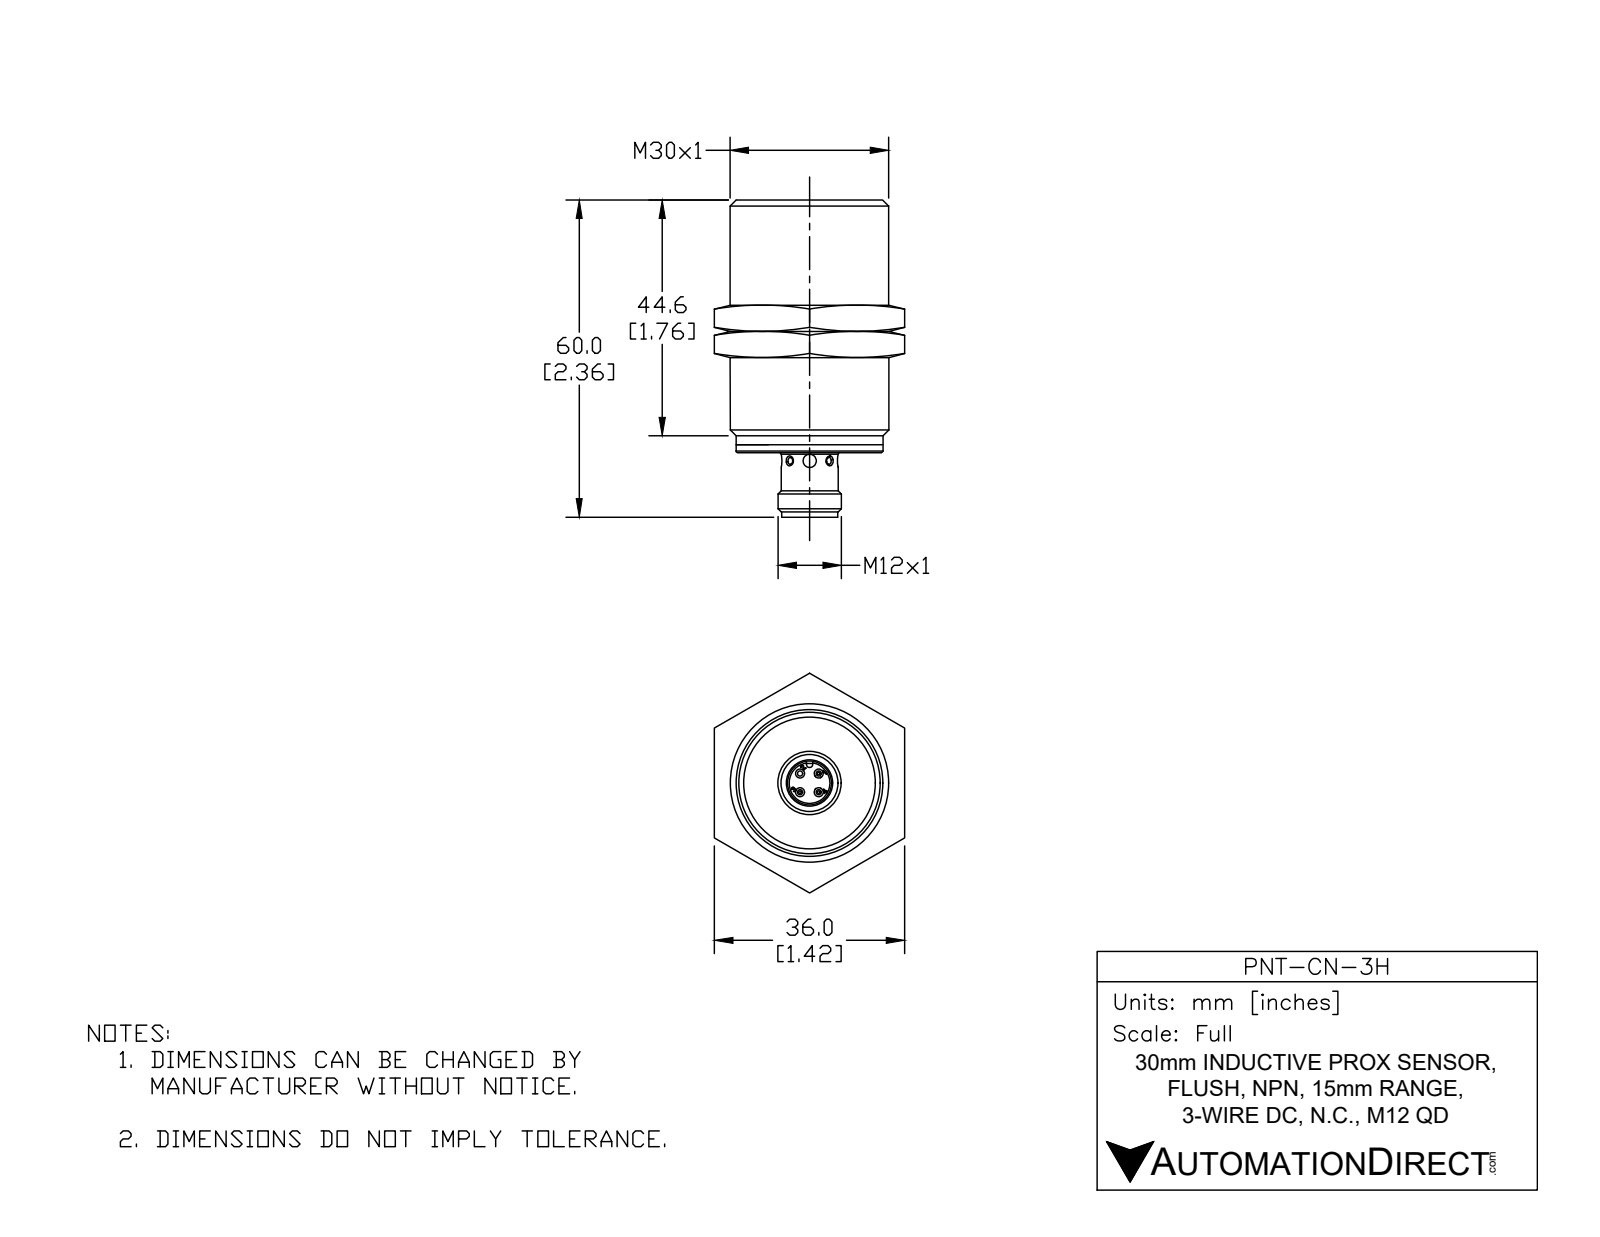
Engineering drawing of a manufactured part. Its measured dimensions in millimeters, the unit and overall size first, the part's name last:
Units: millimetres
Overall size (bounding box): 60 × 30 × 30
Round holes (diameter × count): ⌀1.1 ×3, ⌀1 ×2, ⌀2.5 ×2, ⌀1 ×1, ⌀1 ×1, ⌀8.2 ×1, ⌀8.3 ×1, ⌀10 ×1, ⌀26.6 ×1, ⌀27.3 ×1
Round bosses / shafts (diameter × count): ⌀1 ×9, ⌀30 ×1, ⌀27.8 ×1, ⌀27.5 ×1, ⌀27.3 ×1, ⌀26.5 ×1, ⌀26.3 ×1, ⌀25.9 ×1
Partial cylindrical surfaces — rounded edges, fillets, slot ends (radius × count): R0.1 ×12, R0.5 ×8, R4 ×6, R0.8 ×3, R1 ×3, R0.6 ×1, R0.8 ×1
Main face-to-face distances: 4, 47.8, 43.8, 0.9, 3, 46.8, 47.1, 3.3, 0.8, 0.7
Hole centre spacings: 2.5, 3.5, 5
Volume: 31 690 mm³ · Surface area: 16 240 mm²
Bodies: 1 solid, 660 faces (260 planar, 164 cylindrical, 236 other)
Part name (STEP PRODUCT): PNT-CN-3H
STEP written by: SolidWorks 2017 (AUTOMOTIVE_DESIGN)
